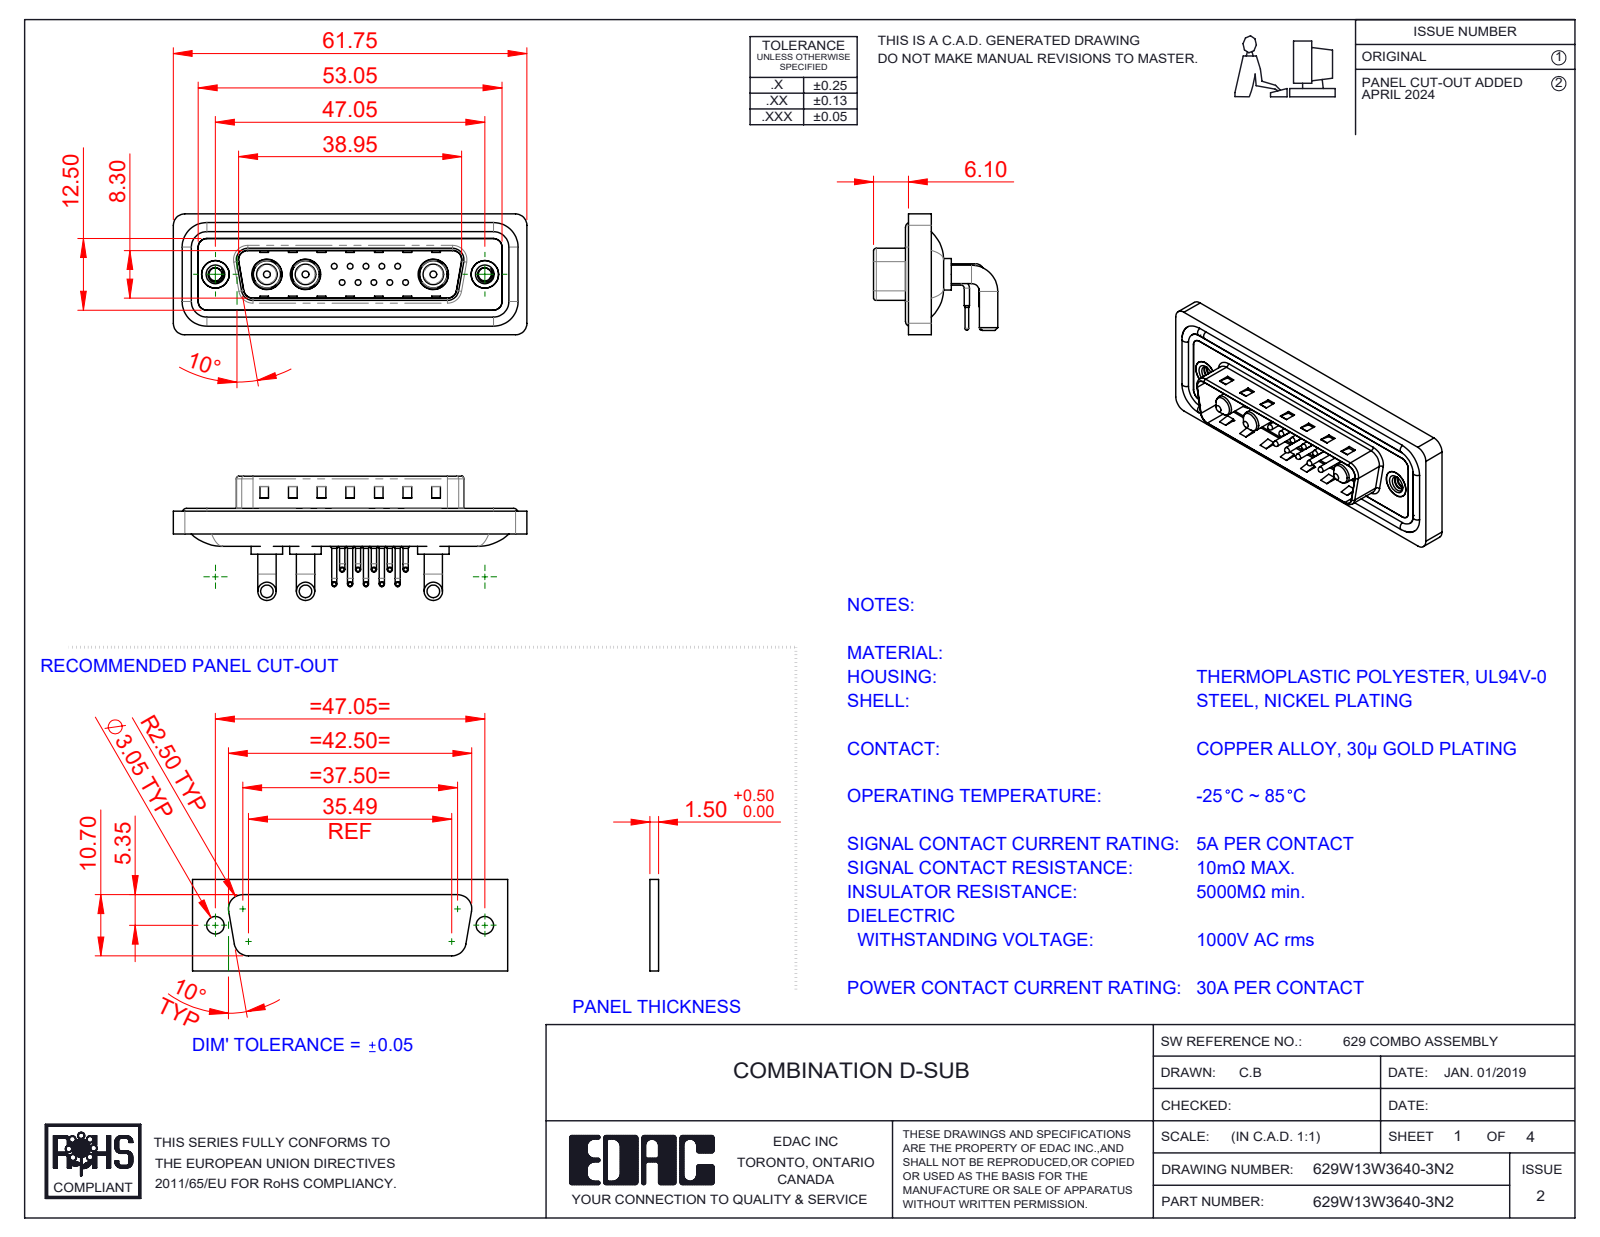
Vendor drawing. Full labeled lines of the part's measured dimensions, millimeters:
Part name (STEP PRODUCT): 629Combo Shell Rear_25 Contacts; 629Combo Shell Front_25 Contacts; Power Pin_30A RA; 629Combo Contact Row 2 (+5 more)
STEP written by: SolidWorks 2023 (CONFIG_CONTROL_DESIGN)
Units: millimetres
Bodies: 23 solids, 1712 faces (879 planar, 611 cylindrical, 222 other)
Overall size (bounding box): 61.75 × 21.7 × 21.1
Volume: 7 705 mm³ · Surface area: 12 552 mm²
Round holes (diameter × count): ⌀0.75 ×10, ⌀1.6 ×10, ⌀2 ×10, ⌀4.85 ×3, ⌀5.3 ×3, ⌀2.26 ×2, ⌀4 ×2, ⌀4.8 ×2, ⌀5 ×2
Round bosses / shafts (diameter × count): ⌀0.9 ×20, ⌀1.5 ×10, ⌀1 ×10, ⌀0.65 ×10, ⌀3.2 ×6, ⌀1.6 ×4, ⌀5.5 ×3, ⌀5.2 ×3
Partial cylindrical surfaces — rounded edges, fillets, slot ends (radius × count): R1.5 ×18, R2 ×18, R1.01 ×10, R0.5 ×8, R1.6 ×8, R0.25 ×4, R0.6 ×4, R0.65 ×4
Main face-to-face distances: 0.4, 2.9, 0.8, 4.1, 1.1, 2.1, 1.6, 4.5, 1.5, 2.5
Hole centre spacings: 3.16, 2.77, 5.04, 5.54, 7.49, 5.03, 8.31, 10.11
